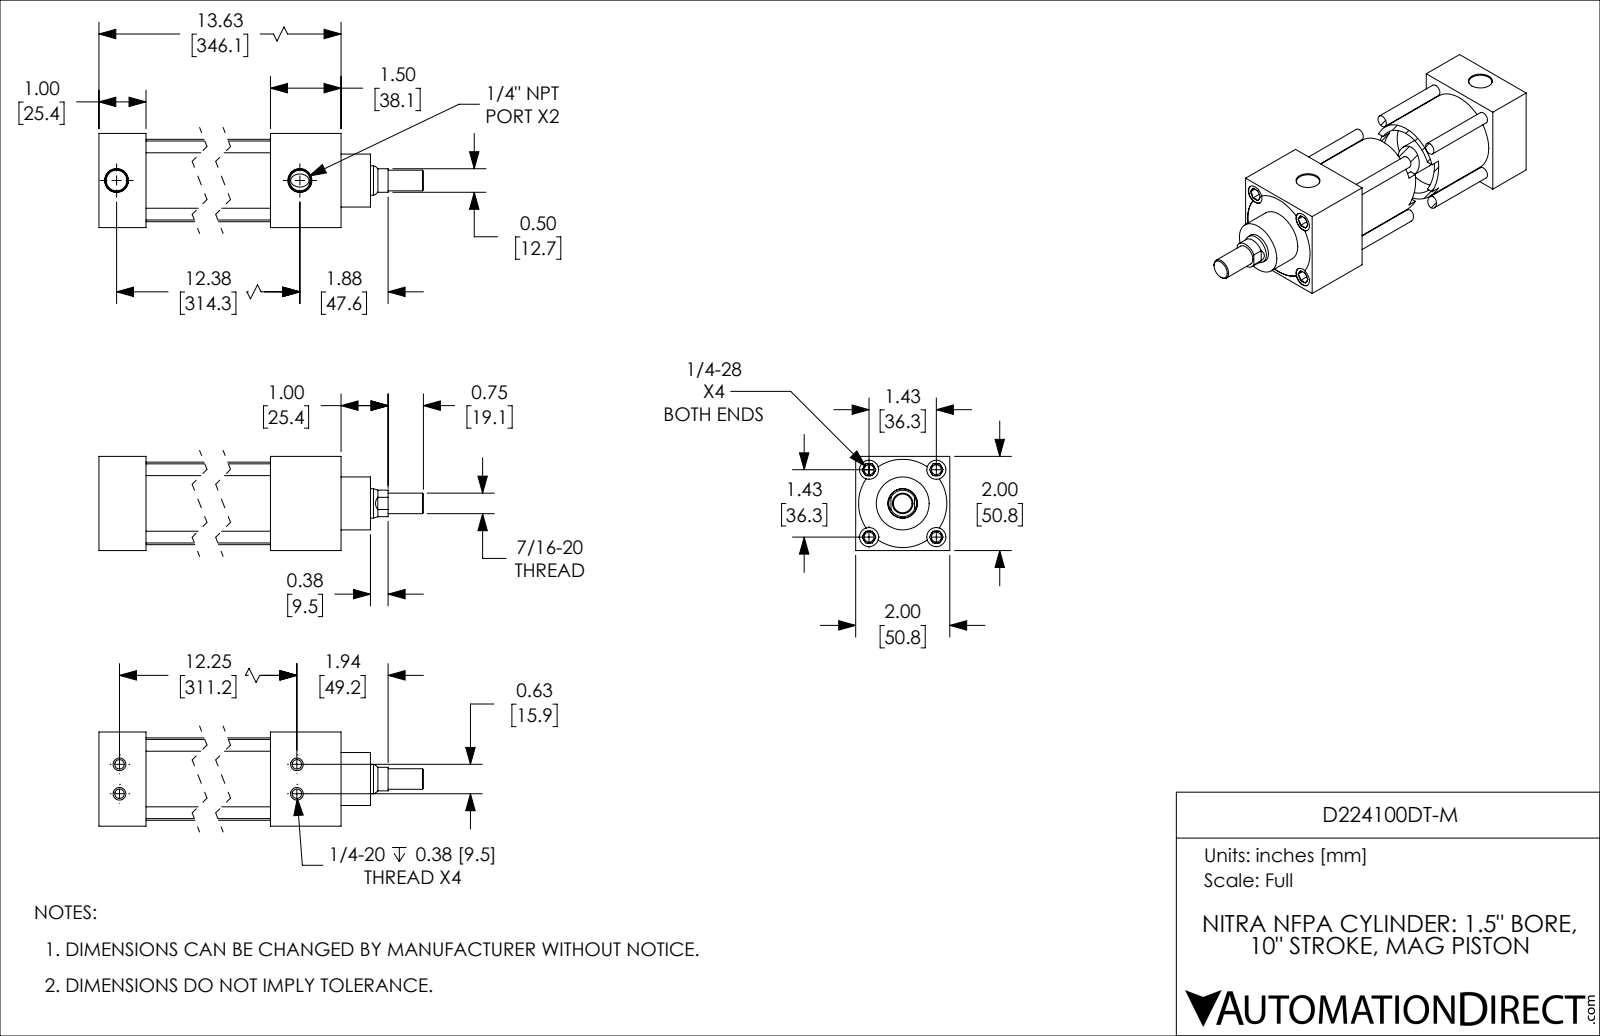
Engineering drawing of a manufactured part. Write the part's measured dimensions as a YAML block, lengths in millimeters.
part_name: "D224100DT-M_BODY; D224100DT-M; D224100DT-M_PISTON_KK1"
step_written_by: "SolidWorks 2019 (CONFIG_CONTROL_DESIGN)"
units: millimeters
bodies: {solids: 2, faces: 203, planar: 58, cylindrical: 65, other: 80}
overall_size: [390.5, 50.8, 50.8]
volume: 403000
surface_area: 148700
round_holes:
  - {diameter: 5.1, count: 4}
  - {diameter: 5.4, count: 4}
  - {diameter: 10.3, count: 4}
  - {diameter: 11.1, count: 2}
  - {diameter: 15.9, count: 1}
  - {diameter: 38.1, count: 1}
round_bosses_or_shafts:
  - {diameter: 6.4, count: 4}
  - {diameter: 44.5, count: 1}
  - {diameter: 38.1, count: 1}
  - {diameter: 28.6, count: 1}
  - {diameter: 15.8, count: 1}
  - {diameter: 11.1, count: 1}
partial_cylinders:
  - {radius: 7.1, count: 1}
  - {radius: 23.8, count: 1}
face_to_face_distances: [50.8, 25.4, 308, 282.6, 345.9, 320.5, 38, 28.6, 54, 254]
hole_center_spacings: [8.1, 25.7, 36.3, 15.9, 51.4, 311.2, 311.6, 312.8]
